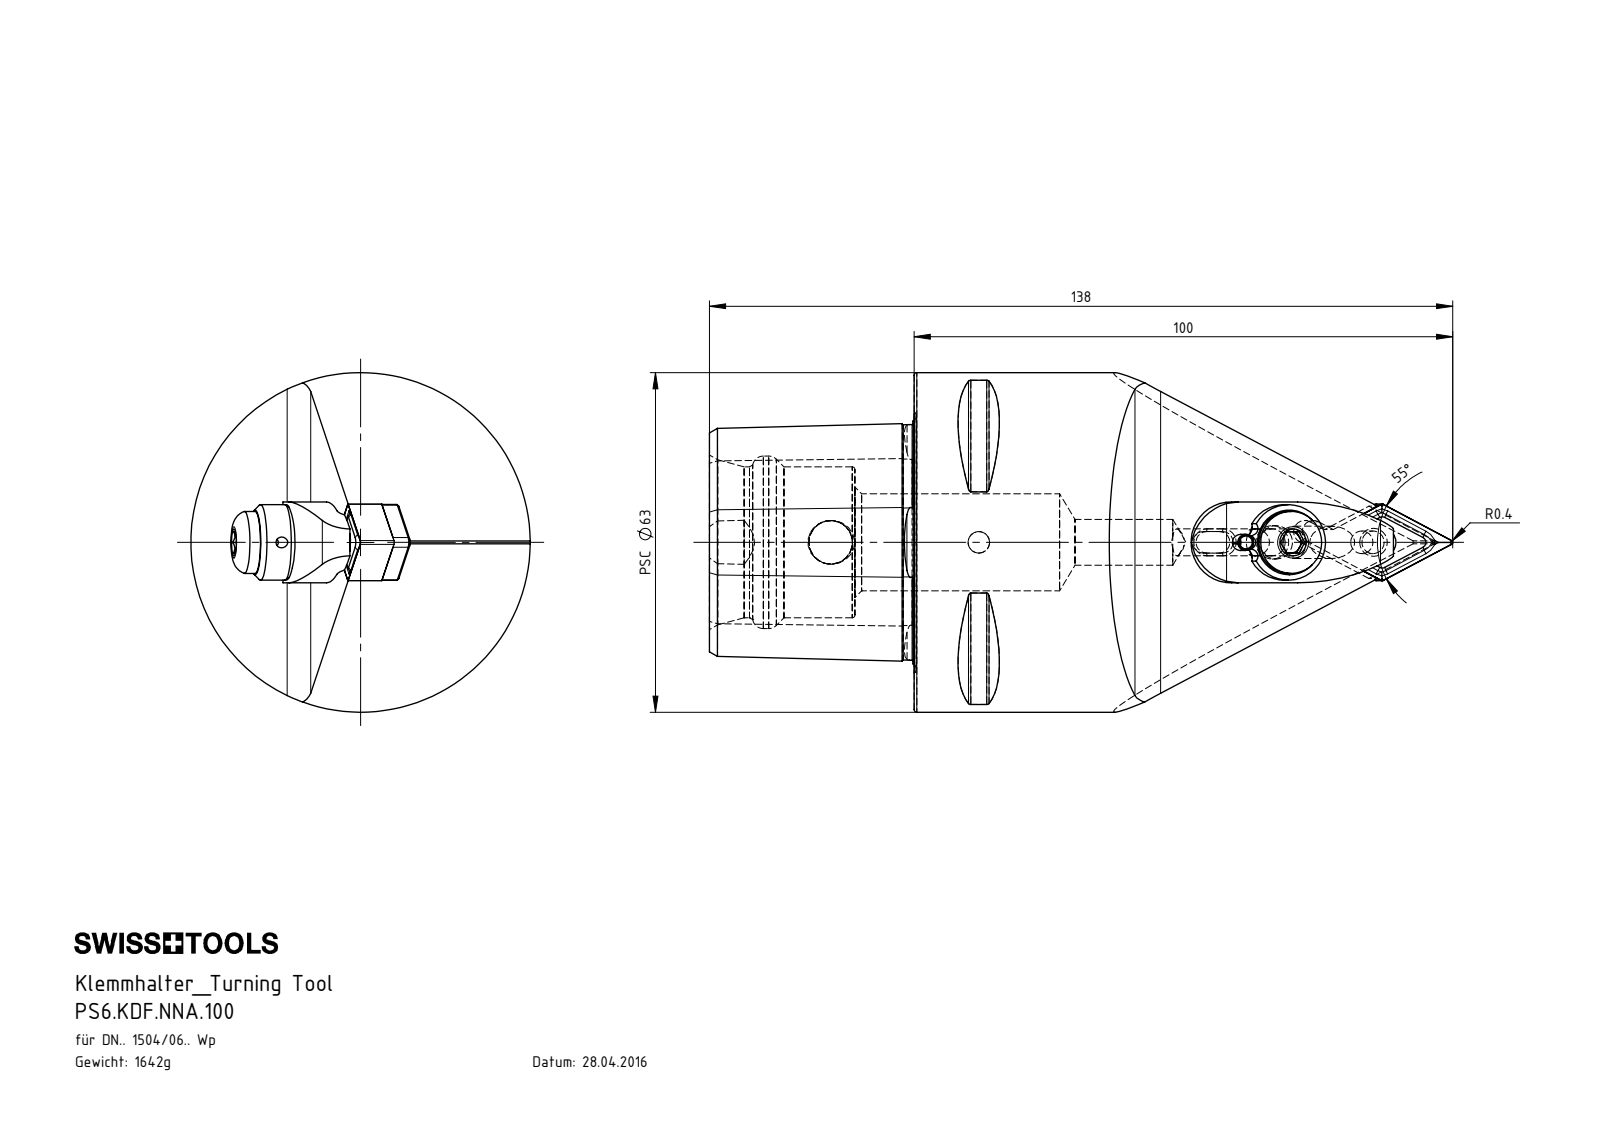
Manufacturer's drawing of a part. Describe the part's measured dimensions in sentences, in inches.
The part is named "PS6-KDF.NNA.100; ISO 13337 - 3 x 12_PreviewCfg; KVT_MB_600_060; WCC-ER5.102.012_B (+7 more)". Its 3-D file was written by "SolidWorks 2012 (CONFIG_CONTROL_DESIGN)". It is 11 solids with 428 faces: 96 planar, 132 cylindrical and 200 other. Overall it measures 5.433 by 2.48 by 2.48 inches. Its volume is 12.82 cubic inches and its surface area 57.05 square inches. Round holes: 3 of diameter 0.079, 3 of diameter 0.197, 2 of diameter 0.276, 2 of diameter 0.335, 1 of diameter 0.094, 1 of diameter 0.118, 1 of diameter 0.157, 1 of diameter 0.165, 1 of diameter 0.203, 1 of diameter 0.236, 1 of diameter 0.244, 1 of diameter 0.252. Round bosses or shafts: 2 of diameter 0.236, 2 of diameter 0.118, 1 of diameter 2.48, 1 of diameter 0.551, 1 of diameter 0.453, 1 of diameter 0.276, 1 of diameter 0.268, 1 of diameter 0.244. Partial cylindrical surfaces (rounded edges, fillets, slot ends): 8 of radius 0.02, 6 of radius 0.015, 6 of radius 0.027, 4 of radius 0.016, 4 of radius 0.039, 3 of radius 0.059, 2 of radius 0.079, 2 of radius 0.118. The main face-to-face distances are 0.468, 1.496, 0.238, 0.125, 0.363, 0.98, 0.415, 0.289, 0.051, 0.5. The hole center spacings are 0.315, 0.787, 1.102, 0.78, 0.315, 0.323, 0.323, 0.788.
